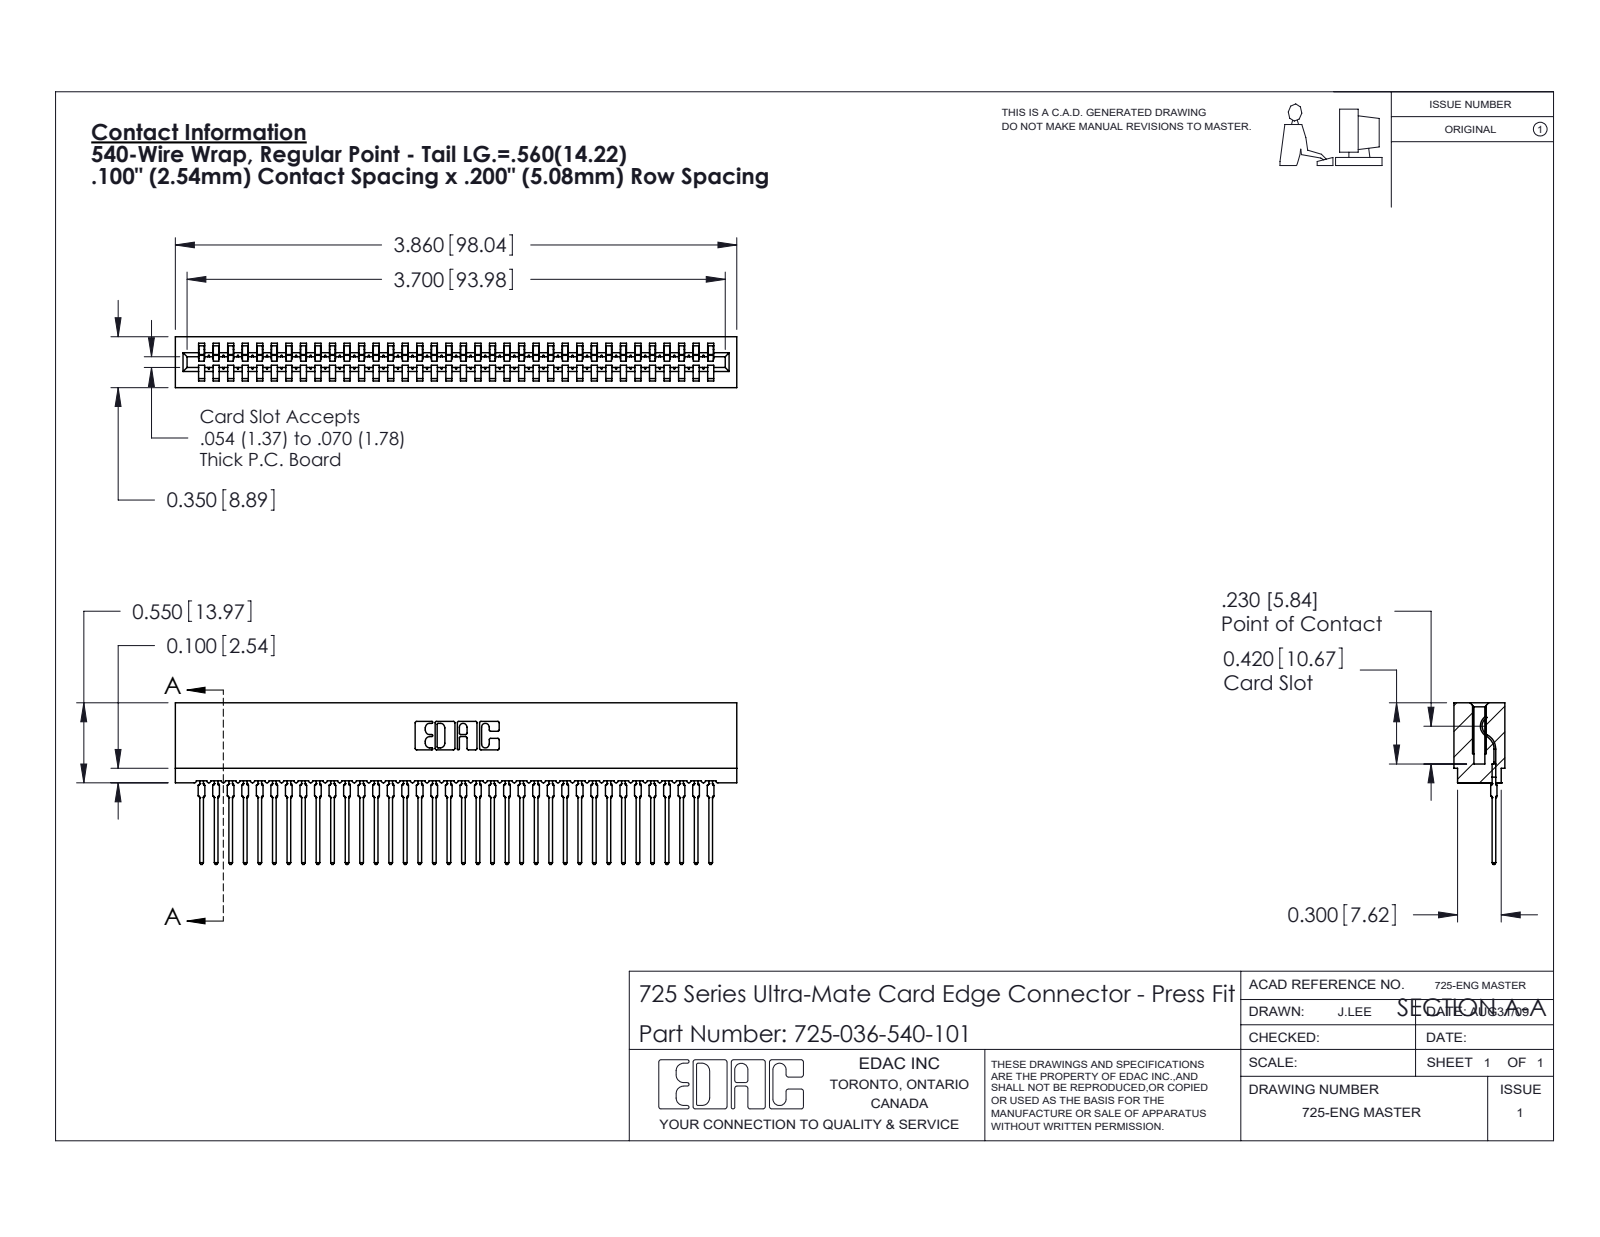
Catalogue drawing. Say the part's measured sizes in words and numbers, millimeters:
The part is named "725 Part_Insulator Option - 01; 745-292-001_540; 725-036-540-101". Its 3-D file was written by "SolidWorks 2020 (CONFIG_CONTROL_DESIGN)". It is 37 solids with 4127 faces: 2467 planar, 724 cylindrical and 936 other. Overall it measures 98 by 28.2 by 8.9 millimeters. Its volume is 7 550 cubic millimeters and its surface area 14 830 square millimeters. Partial cylindrical surfaces (rounded edges, fillets, slot ends): 72 of radius 0.4, 72 of radius 0.5, 22 of radius 0.3, 6 of radius 0.2, 6 of radius 0.8, 4 of radius 0.1, 4 of radius 0.3, 3 of radius 0.7. The main face-to-face distances are 8.9, 5.1, 2.5, 5.4, 3.5, 1.6, 7.3, 1.1, 7.7, 2.4.
